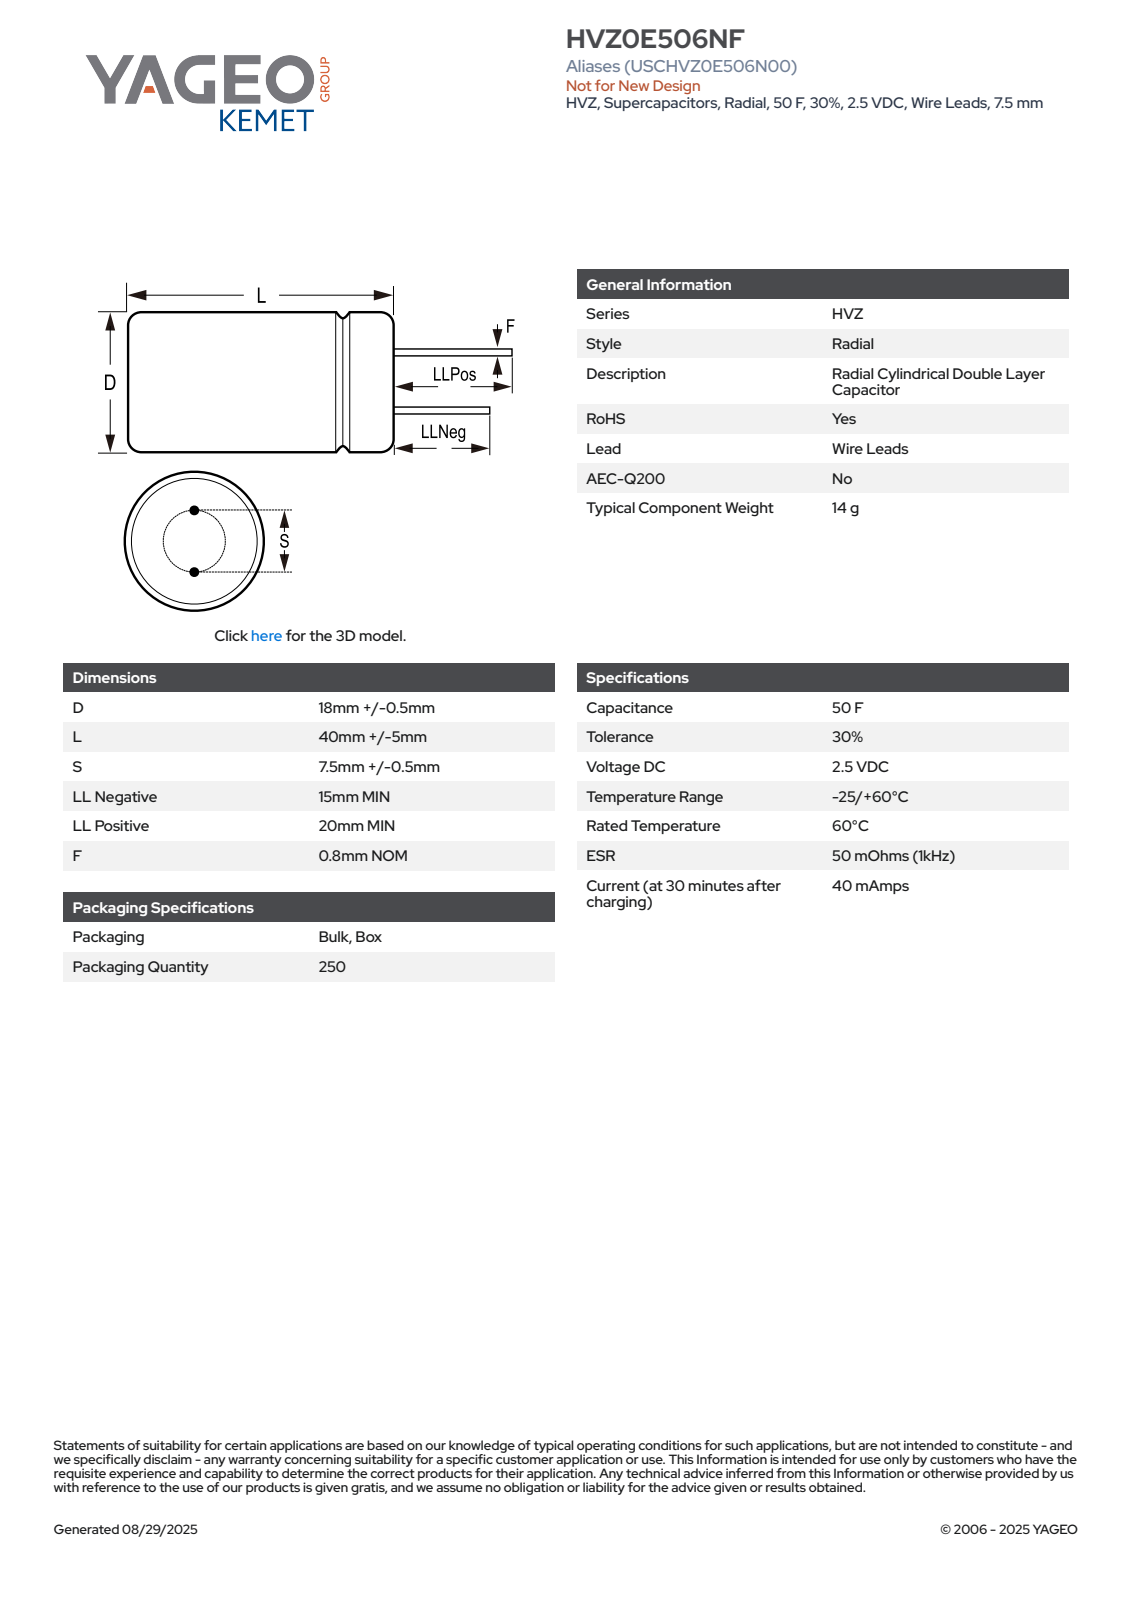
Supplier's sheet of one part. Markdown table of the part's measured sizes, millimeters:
| quantity | value |
| --- | --- |
| part name | CDR_CCW_D18.5L45S7.5F0.8 |
| STEP written by | SolidWorks 2014 (AUTOMOTIVE_DESIGN) |
| units | millimeters |
| bodies | 1 solid, 82 faces (26 planar, 17 cylindrical, 39 other) |
| overall size | 65 × 18.51 × 18.5 |
| volume | 12 073 mm³ |
| surface area | 3 211 mm² |
| round bosses / shafts (diameter × count) | 0.8 × 2, 18.5 × 1 |
| partial cylindrical surfaces (radius × count) | 9.26 × 1 |
| main face-to-face distances | 45, 60, 65, 15, 20, 5 |
